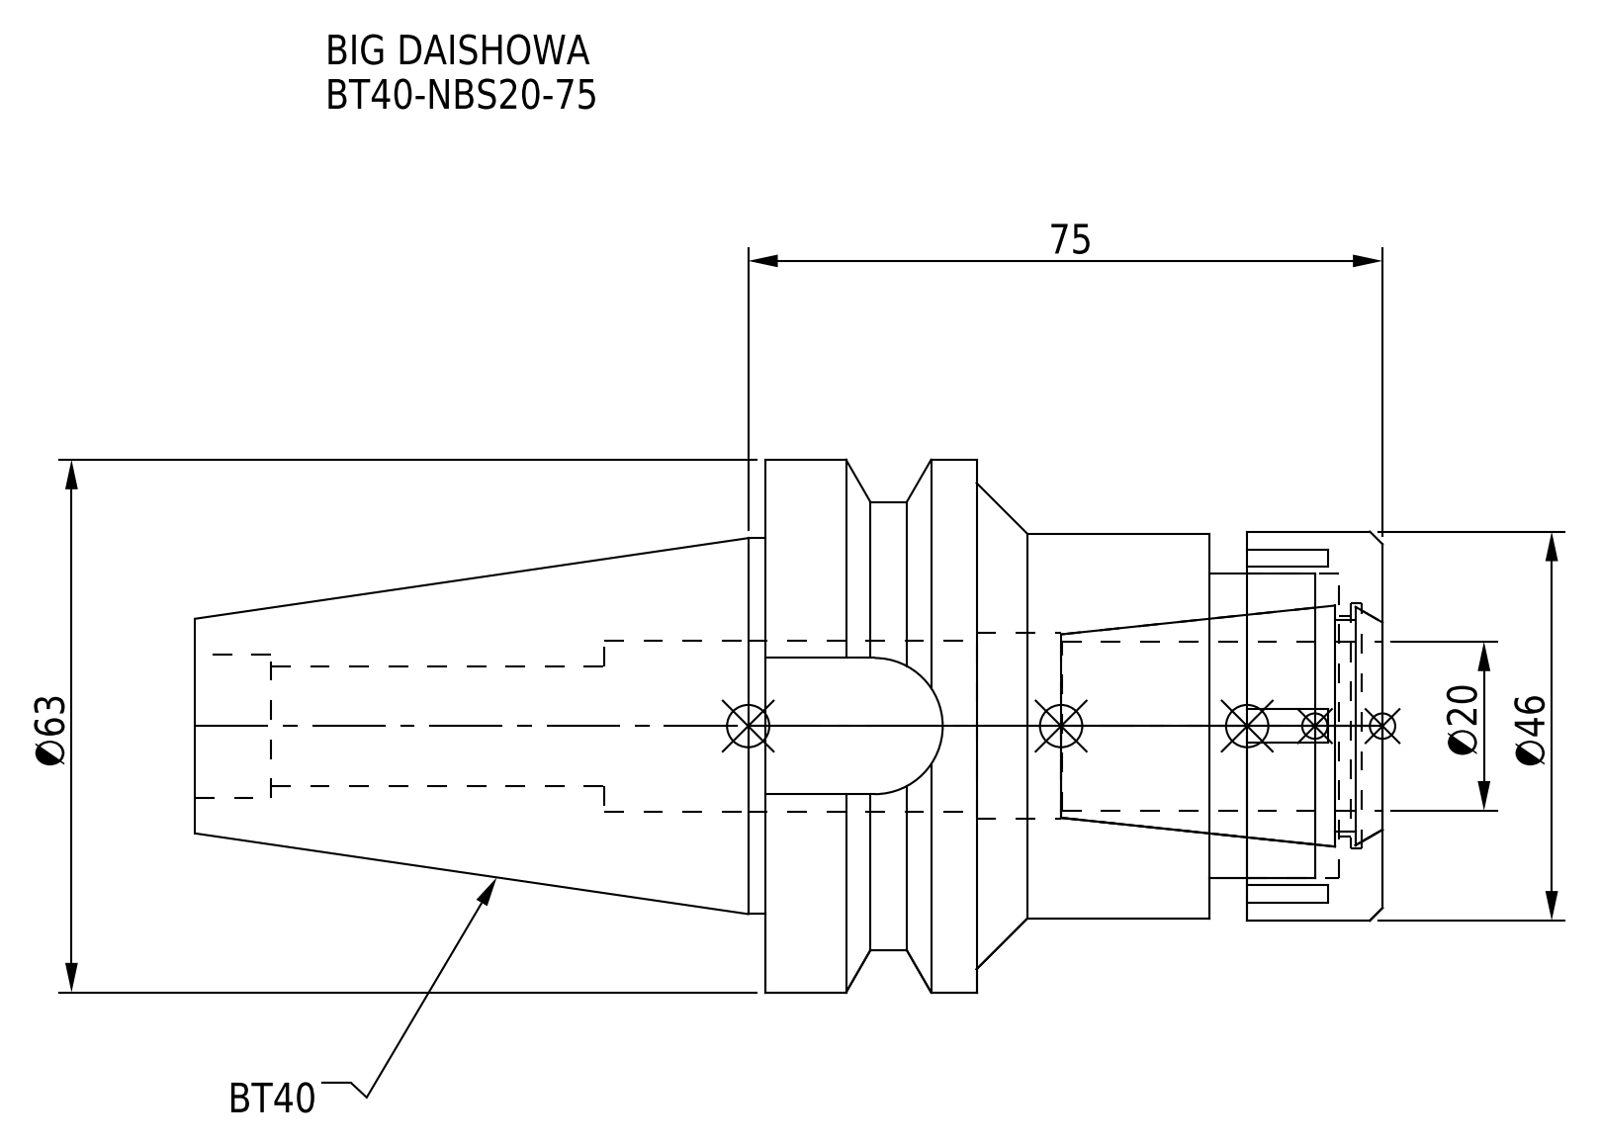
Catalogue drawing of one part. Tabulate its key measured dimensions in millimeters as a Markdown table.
| quantity | value |
| --- | --- |
| part name | BT40-NBS20-75; BT40NB20075-200_ASM.stp; BT40-NBS20-75-FreeParts; NBN20_1.stp (+3 more) |
| STEP written by | SolidWorks 2019 (CONFIG_CONTROL_DESIGN) |
| units | millimeters |
| bodies | 2 solids, 90 faces (44 planar, 32 cylindrical, 14 other) |
| overall size | 140.4 × 63 × 63 |
| volume | 165 429 mm³ |
| surface area | 37 885 mm² |
| round holes (diameter × count) | 14.2 × 1, 17 × 1, 20.3 × 1, 22 × 1, 26 × 1, 29 × 1, 36 × 1 |
| round bosses / shafts (diameter × count) | 63 × 1, 53 × 1, 46 × 1, 45.5 × 1, 44.45 × 1 |
| partial cylindrical surfaces (radius × count) | 8.05 × 1 |
| main face-to-face distances | 73, 8, 20.5, 52.5, 48, 27.5, 25, 16, 4.5, 32 |
